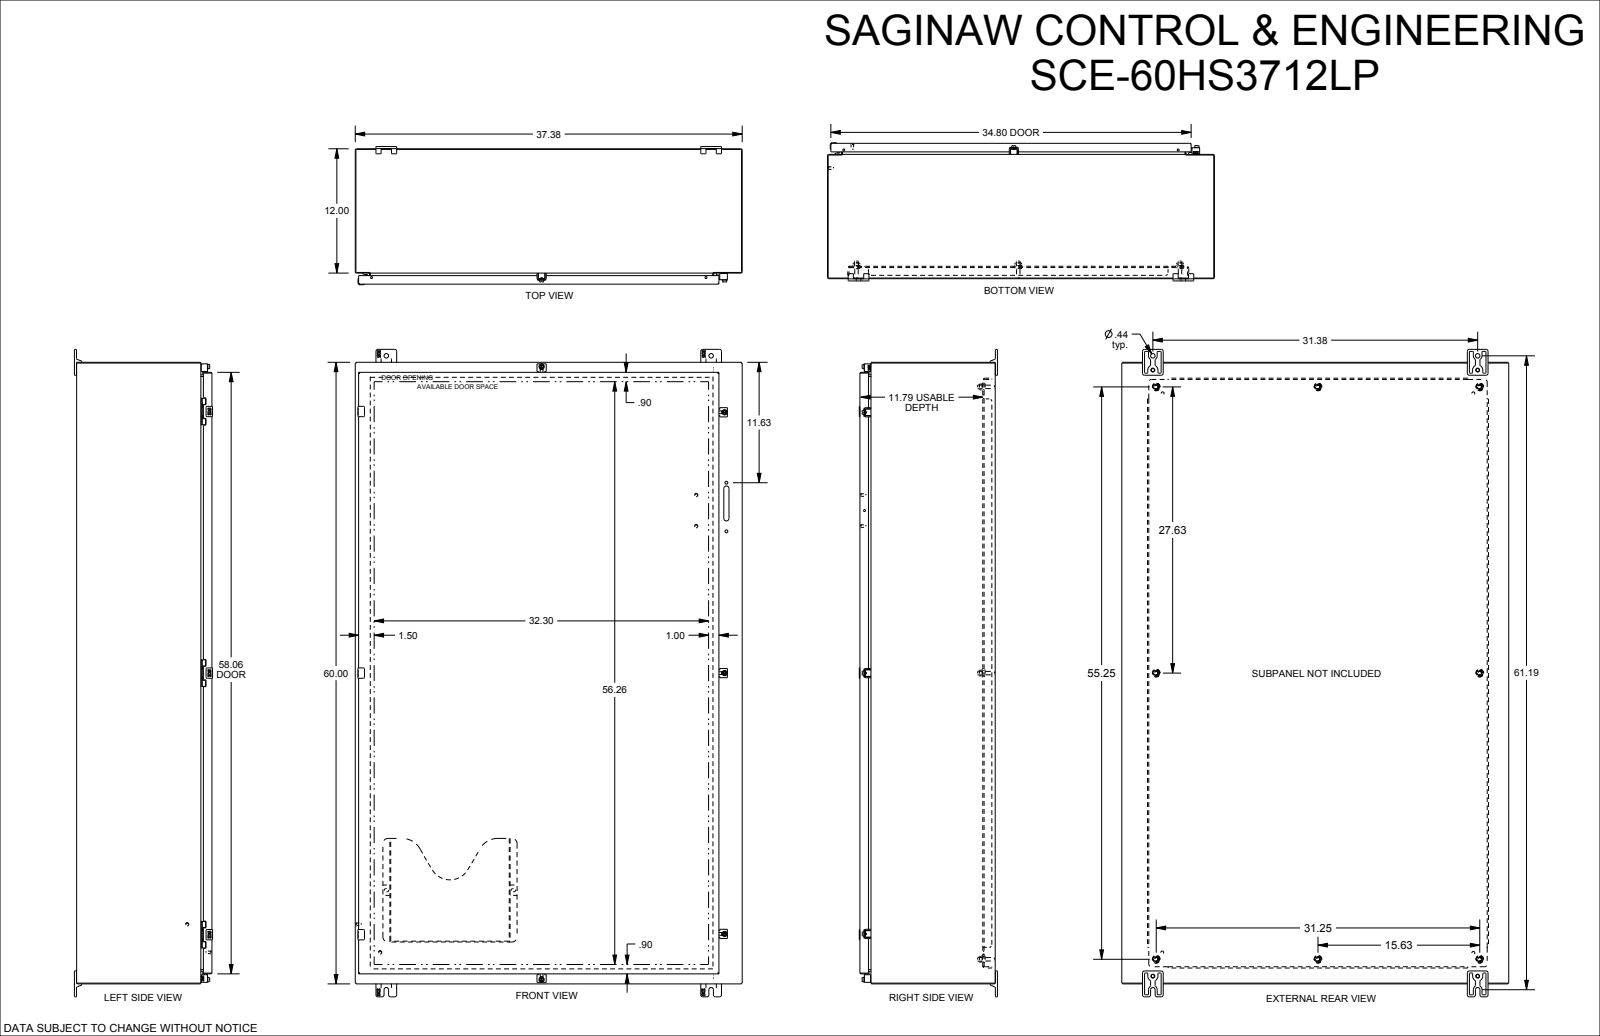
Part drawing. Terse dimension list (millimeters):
name: SCE-60HS3712LP
written by: SolidWorks 2021 (AUTOMOTIVE_DESIGN)
unit: mm
bodies: 47 solids, 2248 faces (886 planar, 897 cylindrical, 465 other)
size: 1587.5 × 949.3 × 344.3
volume: 13 120 000 mm³; area: 12 320 000 mm²
holes: 8× ⌀12.7, 6× ⌀6.8, 6× ⌀7.1, 5× ⌀5.2, 4× ⌀7.9, 4× ⌀11.1, 2× ⌀4.8, 2× ⌀11.1
bosses: 11× ⌀6.3, 8× ⌀9.3, 8× ⌀8.4, 5× ⌀12.9, 5× ⌀6.4, 4× ⌀15, 4× ⌀9.6, 4× ⌀7.9
rounds: 149× R0.3, 88× R0.6, 76× R0.4, 29× R1.5, 20× R1, 20× R4.7, 16× R1.5, 16× R2.5
face distances: 1.9, 1.9, 1.5, 330, 331.9, 330.4, 328.5, 28.6, 30.5, 301.4
hole spacings: 641.4, 701.7, 806.1, 1059.4, 1458.4, 25, 381.5, 686.1
